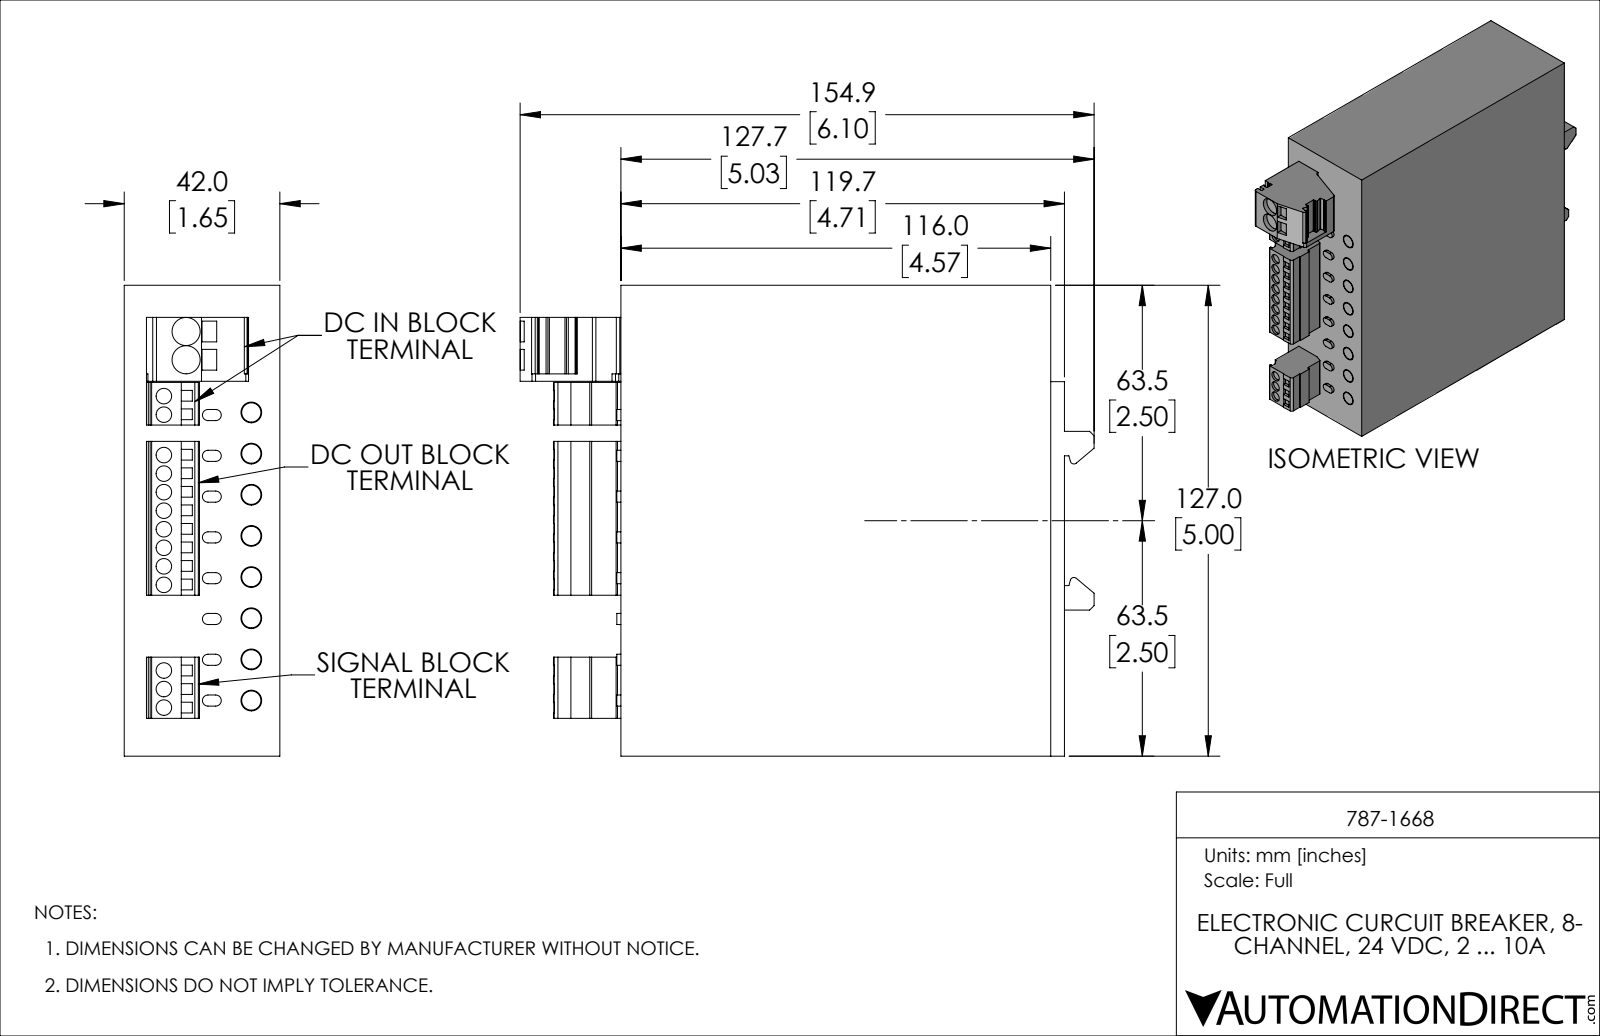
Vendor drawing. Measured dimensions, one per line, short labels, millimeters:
name: 787-1668
written by: PARTsolutions (CONFIG_CONTROL_DESIGN)
unit: mm
bodies: 1 solid, 366 faces (281 planar, 85 cylindrical, 0 other)
size: 154.9 × 127 × 42
volume: 659 662 mm³; area: 60 151 mm²
holes: 13× ⌀4.2, 8× ⌀5.6, 2× ⌀7.6
bosses: 8× ⌀5.2
rounds: 16× R1.5, 12× R0.2, 9× R1, 4× R0.4, 2× R0.3, 2× R0.49
face distances: 42, 127, 119.7, 3.7, 116, 6, 36, 5.05, 36.95, 25.9
hole spacings: 5, 10, 11.1, 22.2, 15, 33.3, 20, 44.4
